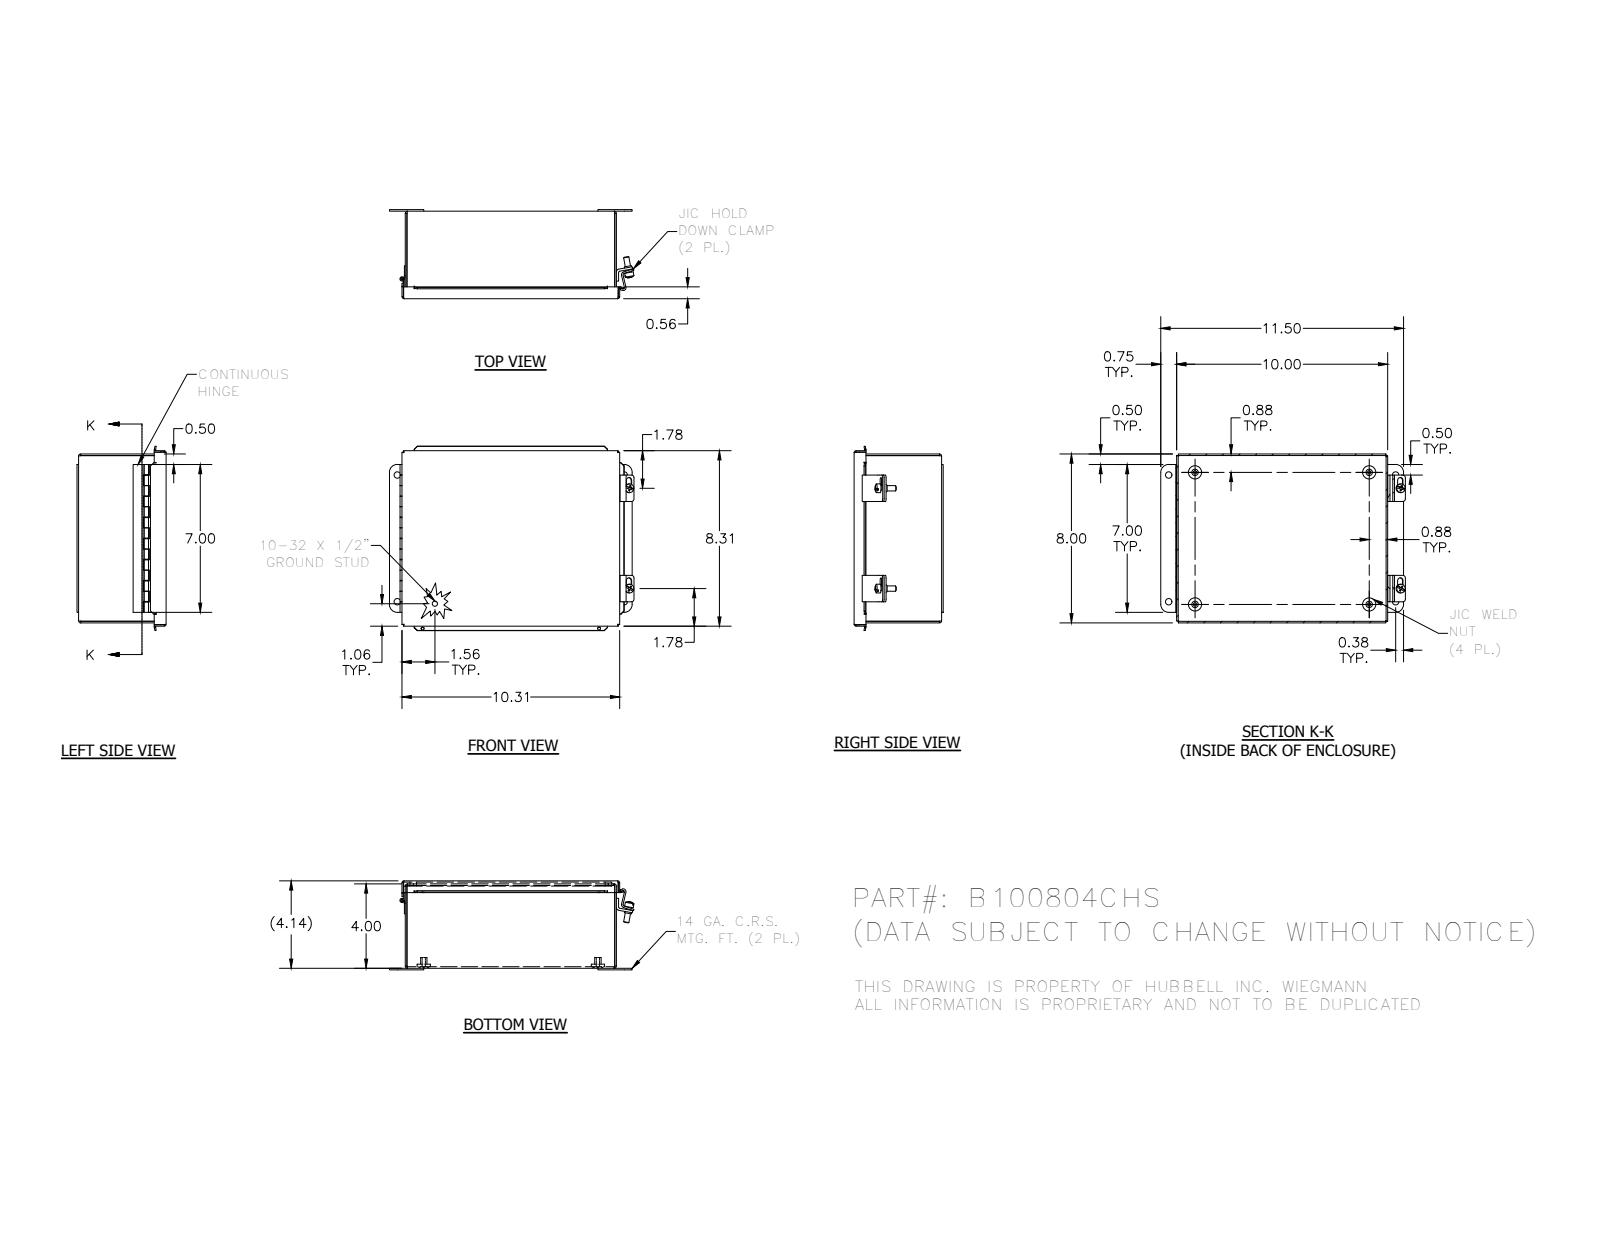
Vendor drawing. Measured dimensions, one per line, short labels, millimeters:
name: B100804CHS; 3499; 3483; C1001 (+8 more)
written by: Autodesk Inventor 2012 (AUTOMOTIVE_DESIGN)
unit: mm
bodies: 20 solids, 459 faces (299 planar, 115 cylindrical, 45 other)
size: 294.3 × 222 × 107.2
volume: 504 100 mm³; area: 539 200 mm²
holes: 4× ⌀4, 4× ⌀7.9, 2× ⌀3.6, 2× ⌀5, 1× ⌀2.9
bosses: 4× ⌀15.9, 4× ⌀7.6, 3× ⌀6.4, 2× ⌀10.4, 2× ⌀8.7, 1× ⌀5.1, 1× ⌀4.8, 1× ⌀2.5
rounds: 15× R0.8, 8× R2.7, 8× R3.2, 7× R2.4, 4× R3.4, 4× R9.5, 3× R1.6, 3× R3.2
face distances: 1.9, 103.7, 1.6, 105.3, 101.8, 103.4, 201.3, 252.1, 203.2, 199.4
hole spacings: 158.8, 31.9, 31.9, 152.4, 241.3, 120.7, 158.8, 158.8
